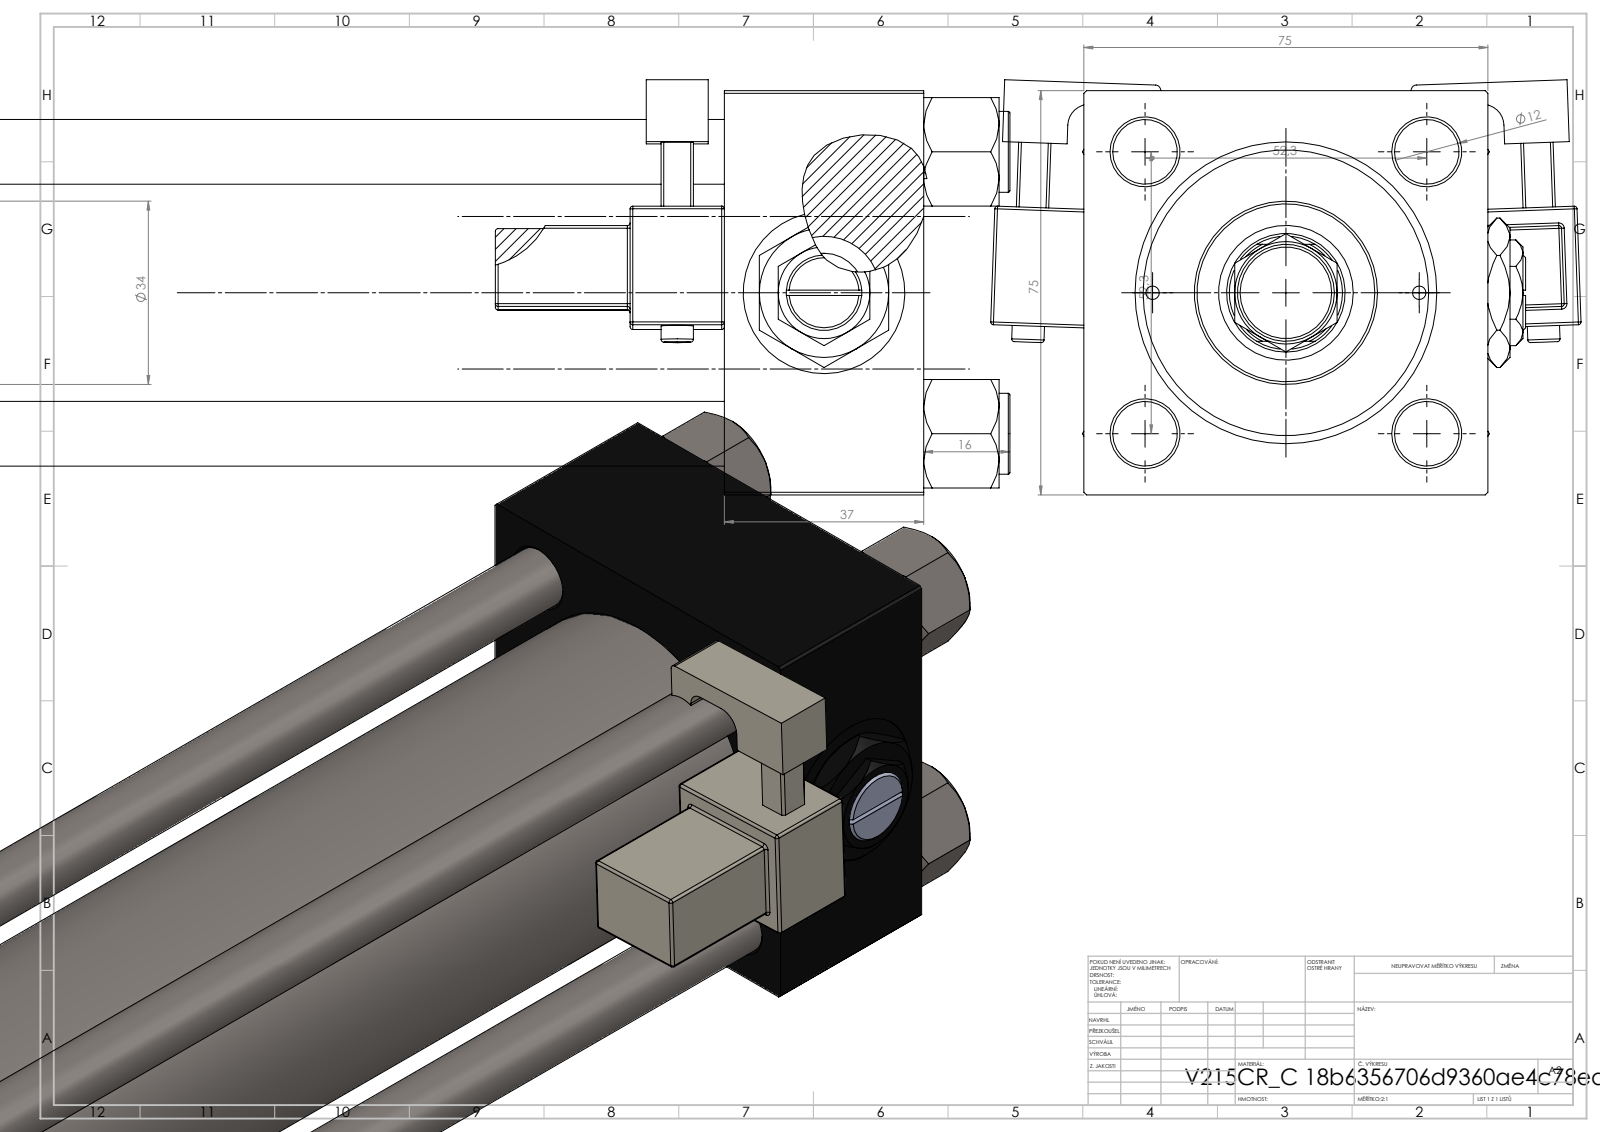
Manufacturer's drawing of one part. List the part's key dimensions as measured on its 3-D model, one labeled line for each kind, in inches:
Part name (STEP PRODUCT): MFA; V215CR_C_Body; V215CR_C_TYCINKA; Zatka_pro_OIL_PORT (+4 more)
STEP written by: SolidWorks 2019 (CONFIG_CONTROL_DESIGN)
Units: inches
Bodies: 16 solids, 1461 faces (649 planar, 166 cylindrical, 646 other)
Overall size (bounding box): 23.937 × 4.314 × 3.033
Volume: 73.66 in³ · Surface area: 584.2 in²
Round holes (diameter × count): ⌀0.472 ×4, ⌀0.098 ×2, ⌀0.276 ×2, ⌀0.825 ×2, ⌀1.181 ×2, ⌀0.413 ×1, ⌀0.866 ×1, ⌀0.984 ×1, ⌀1.614 ×1, ⌀1.969 ×1, ⌀2.087 ×1
Round bosses / shafts (diameter × count): ⌀0.591 ×4, ⌀0.236 ×2, ⌀2.205 ×1, ⌀1.339 ×1, ⌀0.709 ×1, ⌀0.433 ×1
Partial cylindrical surfaces — rounded edges, fillets, slot ends (radius × count): R0.02 ×48, R0.039 ×2, R0.098 ×2, R0.157 ×2, R0.413 ×1
Main face-to-face distances: 2.953, 1.457, 21.024, 19.567, 18.701, 17.244, 2.323, 19.894, 18.437, 1.193
Hole centre spacings: 1.031, 1.456, 2.059, 2.253, 0.974, 2.912, 1.949, 18.642
